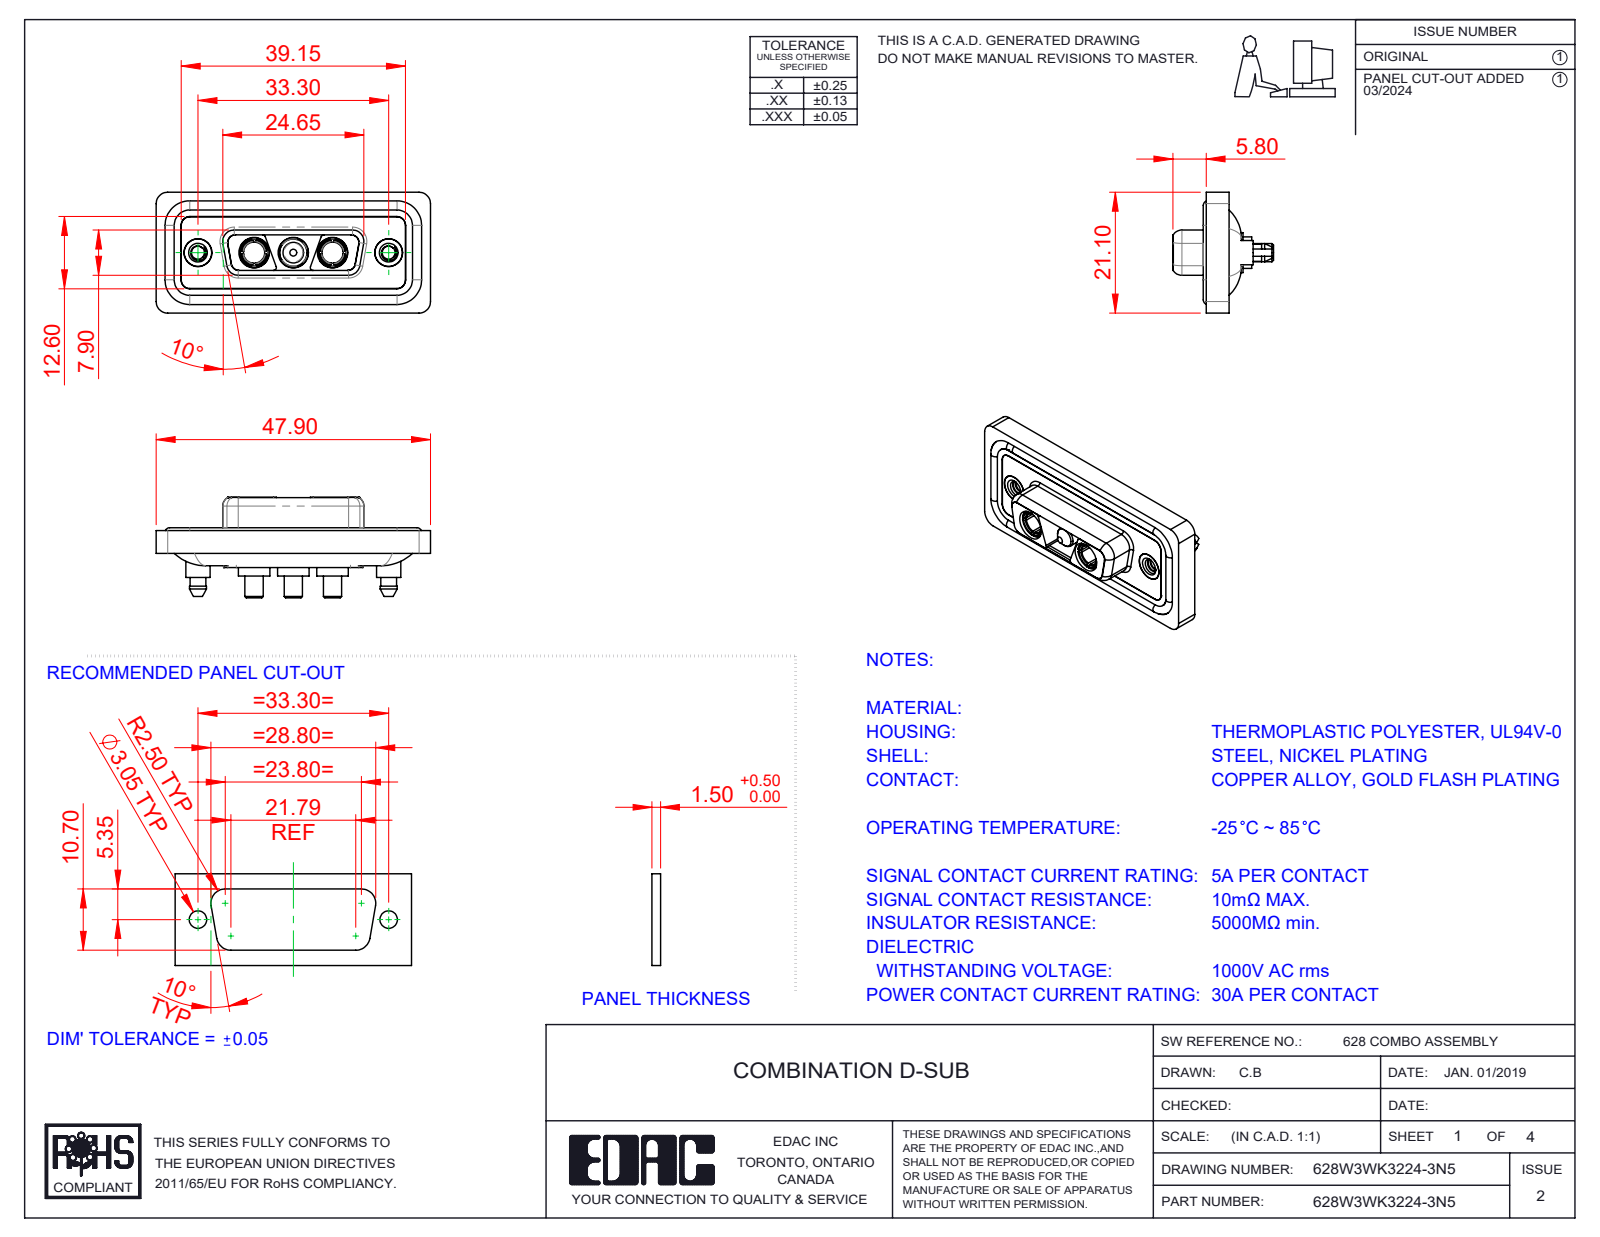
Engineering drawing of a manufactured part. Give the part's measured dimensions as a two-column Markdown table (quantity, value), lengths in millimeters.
| quantity | value |
| --- | --- |
| part name | 628Combo Housing_3WK3; 628Combo Shell Rear_15 Contacts; 628W3WK3224-3N5; Power Pin_30A S (+4 more) |
| STEP written by | SolidWorks 2023 (CONFIG_CONTROL_DESIGN) |
| units | millimeters |
| bodies | 13 solids, 633 faces (194 planar, 290 cylindrical, 149 other) |
| overall size | 47.9 × 21.1 × 17.55 |
| volume | 6 033 mm³ |
| surface area | 9 852 mm² |
| round holes (diameter × count) | 4.85 × 5, 5.3 × 3, 2.26 × 2, 3.7 × 2, 4 × 2, 4.05 × 2, 5 × 2 |
| round bosses / shafts (diameter × count) | 1.6 × 4, 5.5 × 3, 5.2 × 3, 4.75 × 3, 3.75 × 3, 3.2 × 3, 5.4 × 2, 4.96 × 2 |
| partial cylindrical surfaces (radius × count) | 1.5 × 24, 2 × 20, 1.35 × 12, 1.6 × 10, 0.5 × 8, 0.25 × 4, 0.6 × 4, 0.65 × 4 |
| main face-to-face distances | 0.4, 1.6, 1.8, 0.5, 1.1, 2.9, 5.65, 7.05, 1.5, 5.35 |
| hole center spacings | 6.85, 9.8, 16.65, 23.5, 13.7, 33.3 |
